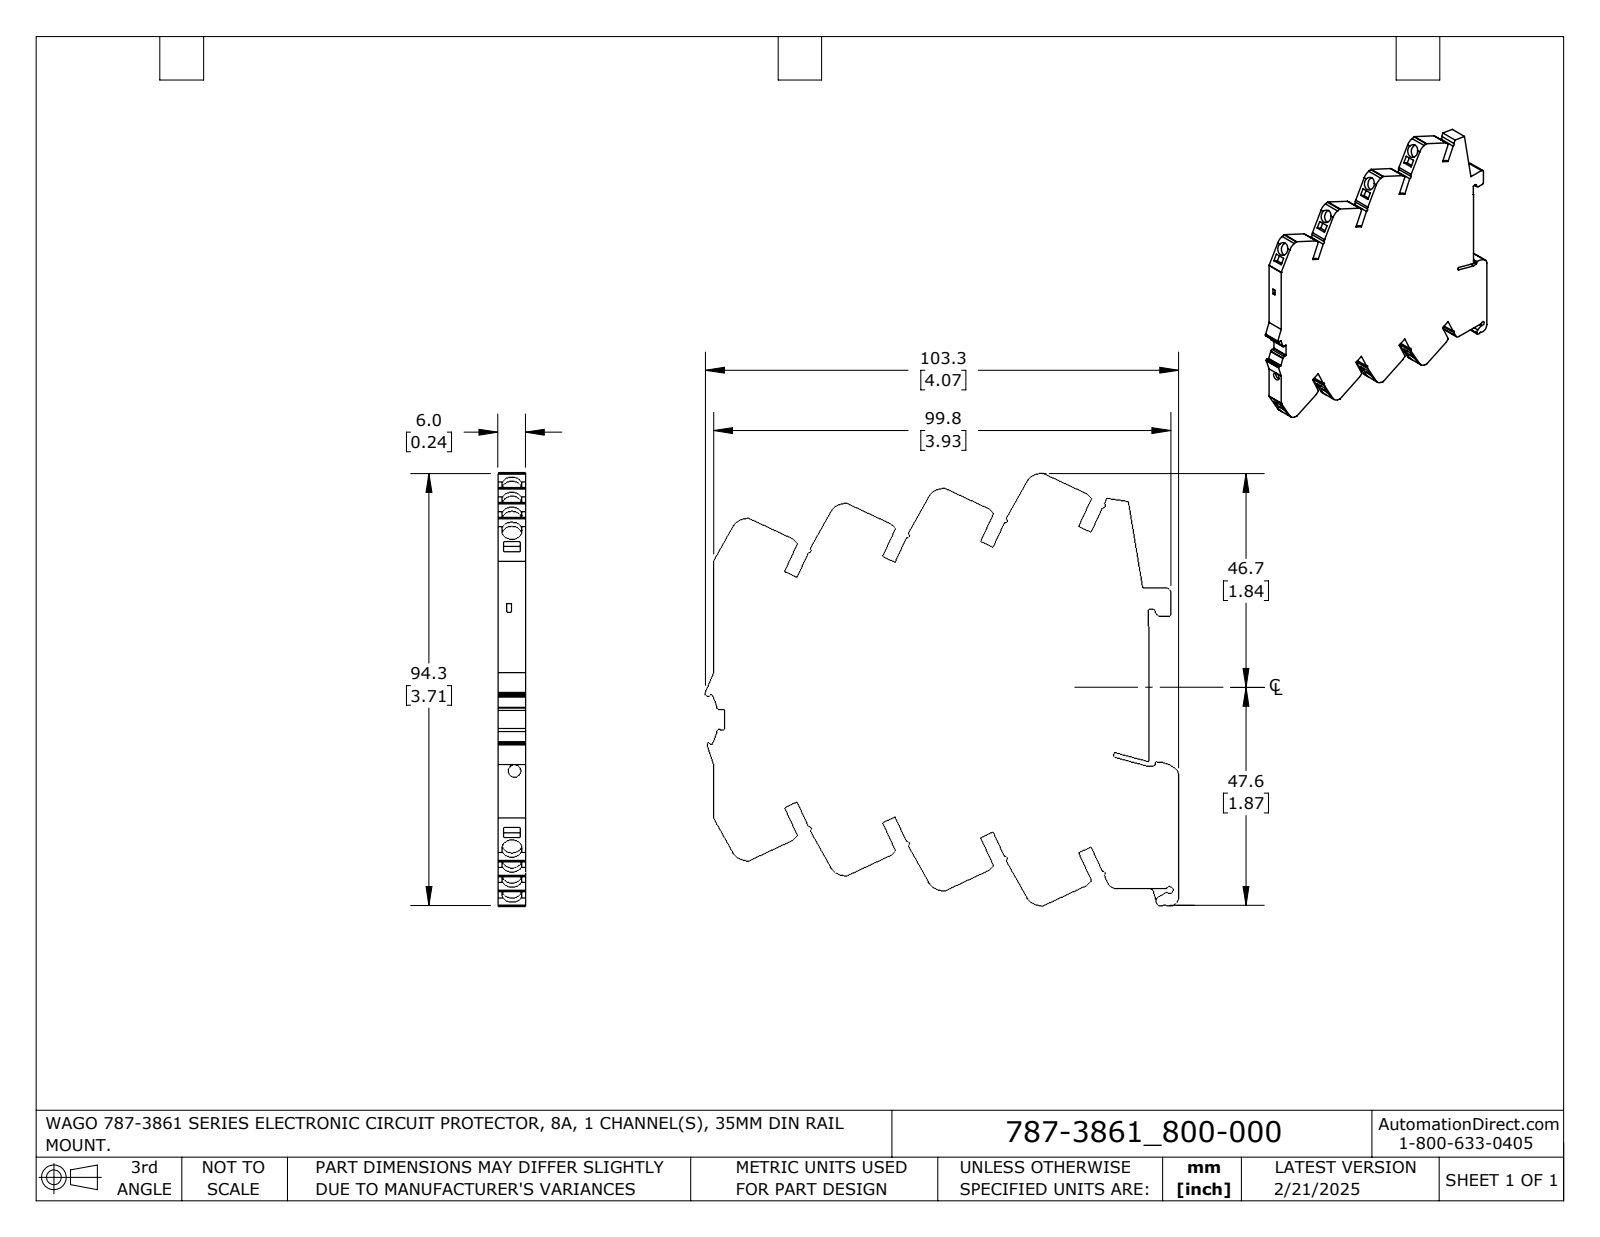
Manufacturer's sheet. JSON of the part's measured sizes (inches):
{"part_name": "787-3861_800-000_HI", "step_written_by": "SolidWorks 2024 (AUTOMOTIVE_DESIGN)", "units": "inches", "bodies": {"solids": 1, "faces": 262, "planar": 197, "cylindrical": 65, "other": 0}, "overall_size": [4.067, 3.711, 0.236], "volume_in3": 2.685, "surface_area_in2": 29.24, "round_holes": [[0.173, 8], [0.106, 1]], "partial_cylinders_radius": [[0.008, 13], [0.02, 12], [0.016, 8], [0.132, 8], [0.039, 5], [0.012, 3], [0.079, 3], [0.018, 2]], "face_to_face_distances": [0.236, 0.708, 0.67, 0.473, 0.118, 1.417, 0.472, 0.945, 0.59, 1.34], "hole_center_spacings": [0.526, 0.525, 1.051, 1.052, 1.577]}
